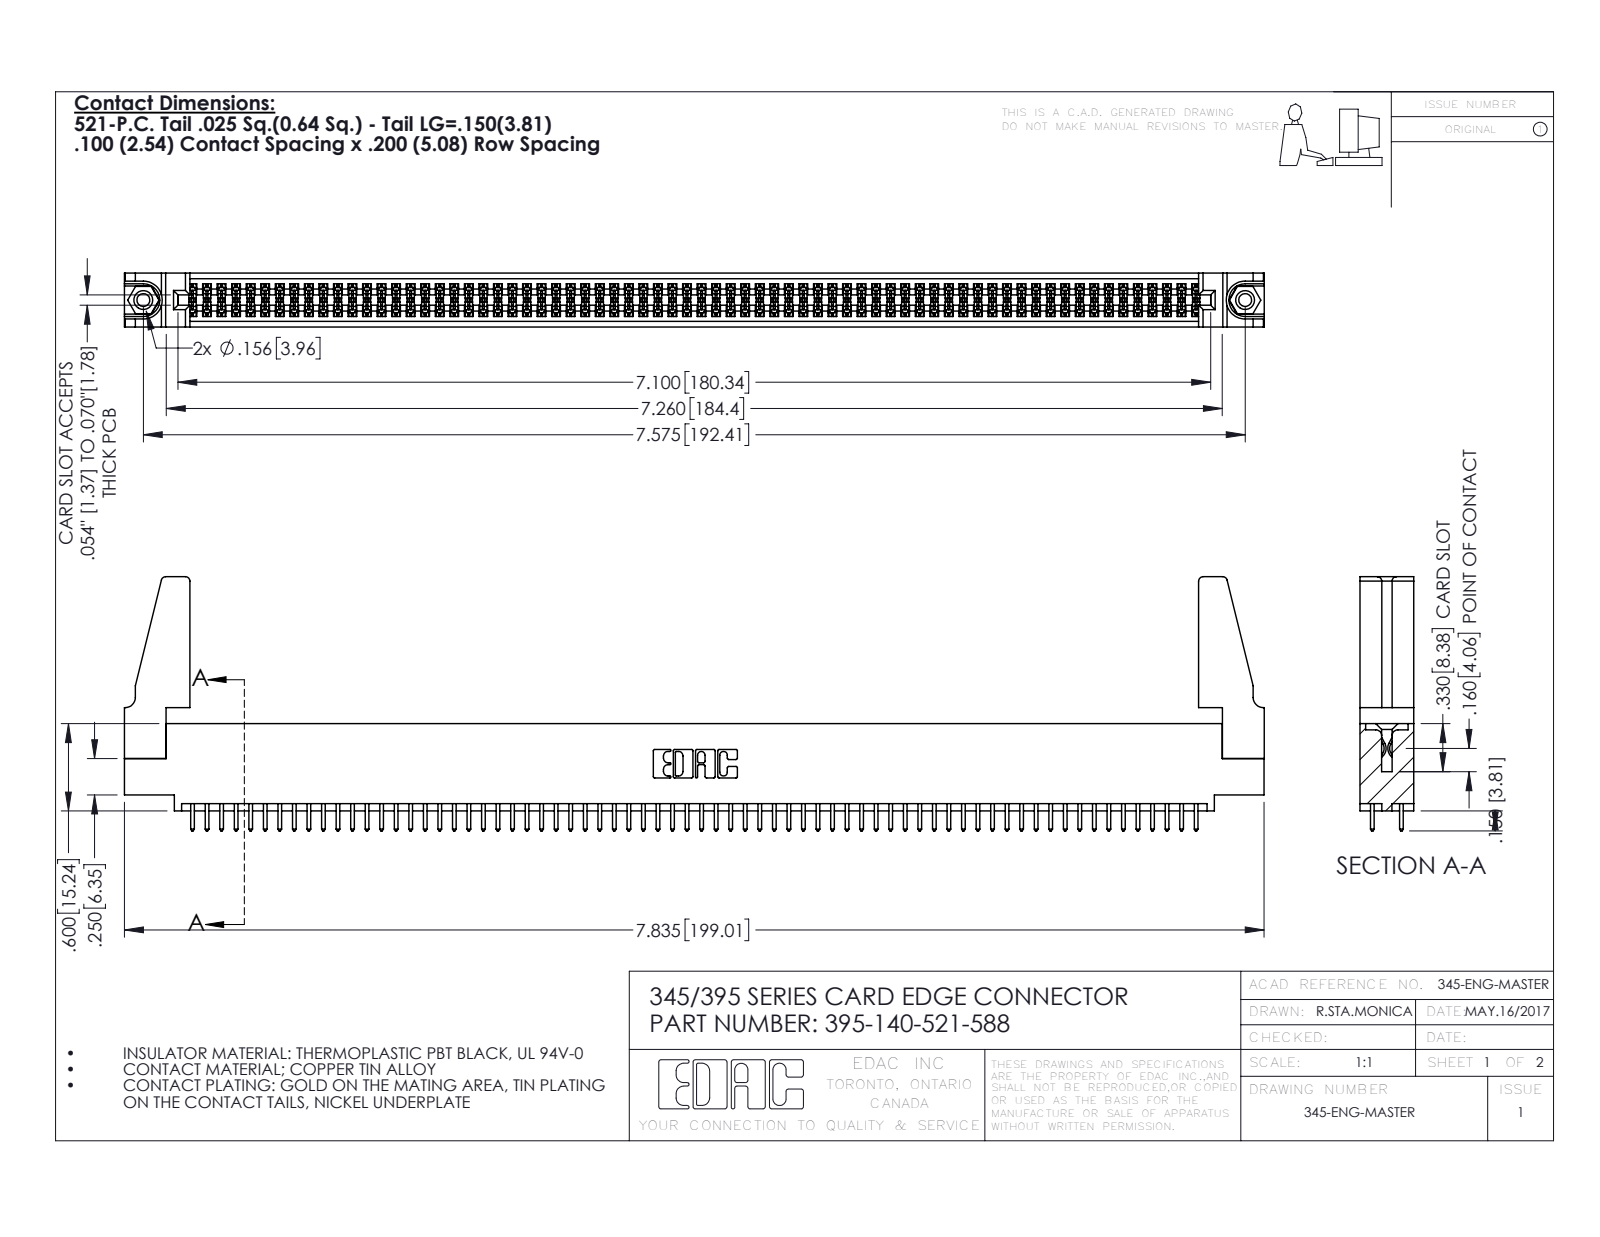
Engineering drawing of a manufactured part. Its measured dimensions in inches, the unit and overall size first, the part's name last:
Units: inches
Overall size (bounding box): 7.836 × 1.747 × 0.37
Round holes (diameter × count): ⌀0.089 ×2, ⌀0.125 ×2, ⌀0.156 ×2, ⌀0.064 ×1
Round bosses / shafts (diameter × count): ⌀0.155 ×2
Partial cylindrical surfaces — rounded edges, fillets, slot ends (radius × count): R0.006 ×210, R0.01 ×140, R0.01 ×22, R0.03 ×8, R0.007 ×6, R0.031 ×6, R0.026 ×3, R0.014 ×2
Main face-to-face distances: 0.072, 0.298, 0.37, 0.2, 0.098, 0.272, 0.025, 0.225, 0.175, 0.149
Hole centre spacings: 0.27, 7.339, 7.575
Volume: 1.386 in³ · Surface area: 49.84 in²
Bodies: 145 solids, 7254 faces (4776 planar, 2462 cylindrical, 16 other)
Part name (STEP PRODUCT): 345-220-078_345-220-088; 345-292-001_345-293-121; 395-140-521-588; 345-250-001_345-250-001-102 (+1 more)
STEP written by: SolidWorks 2016 (CONFIG_CONTROL_DESIGN)
